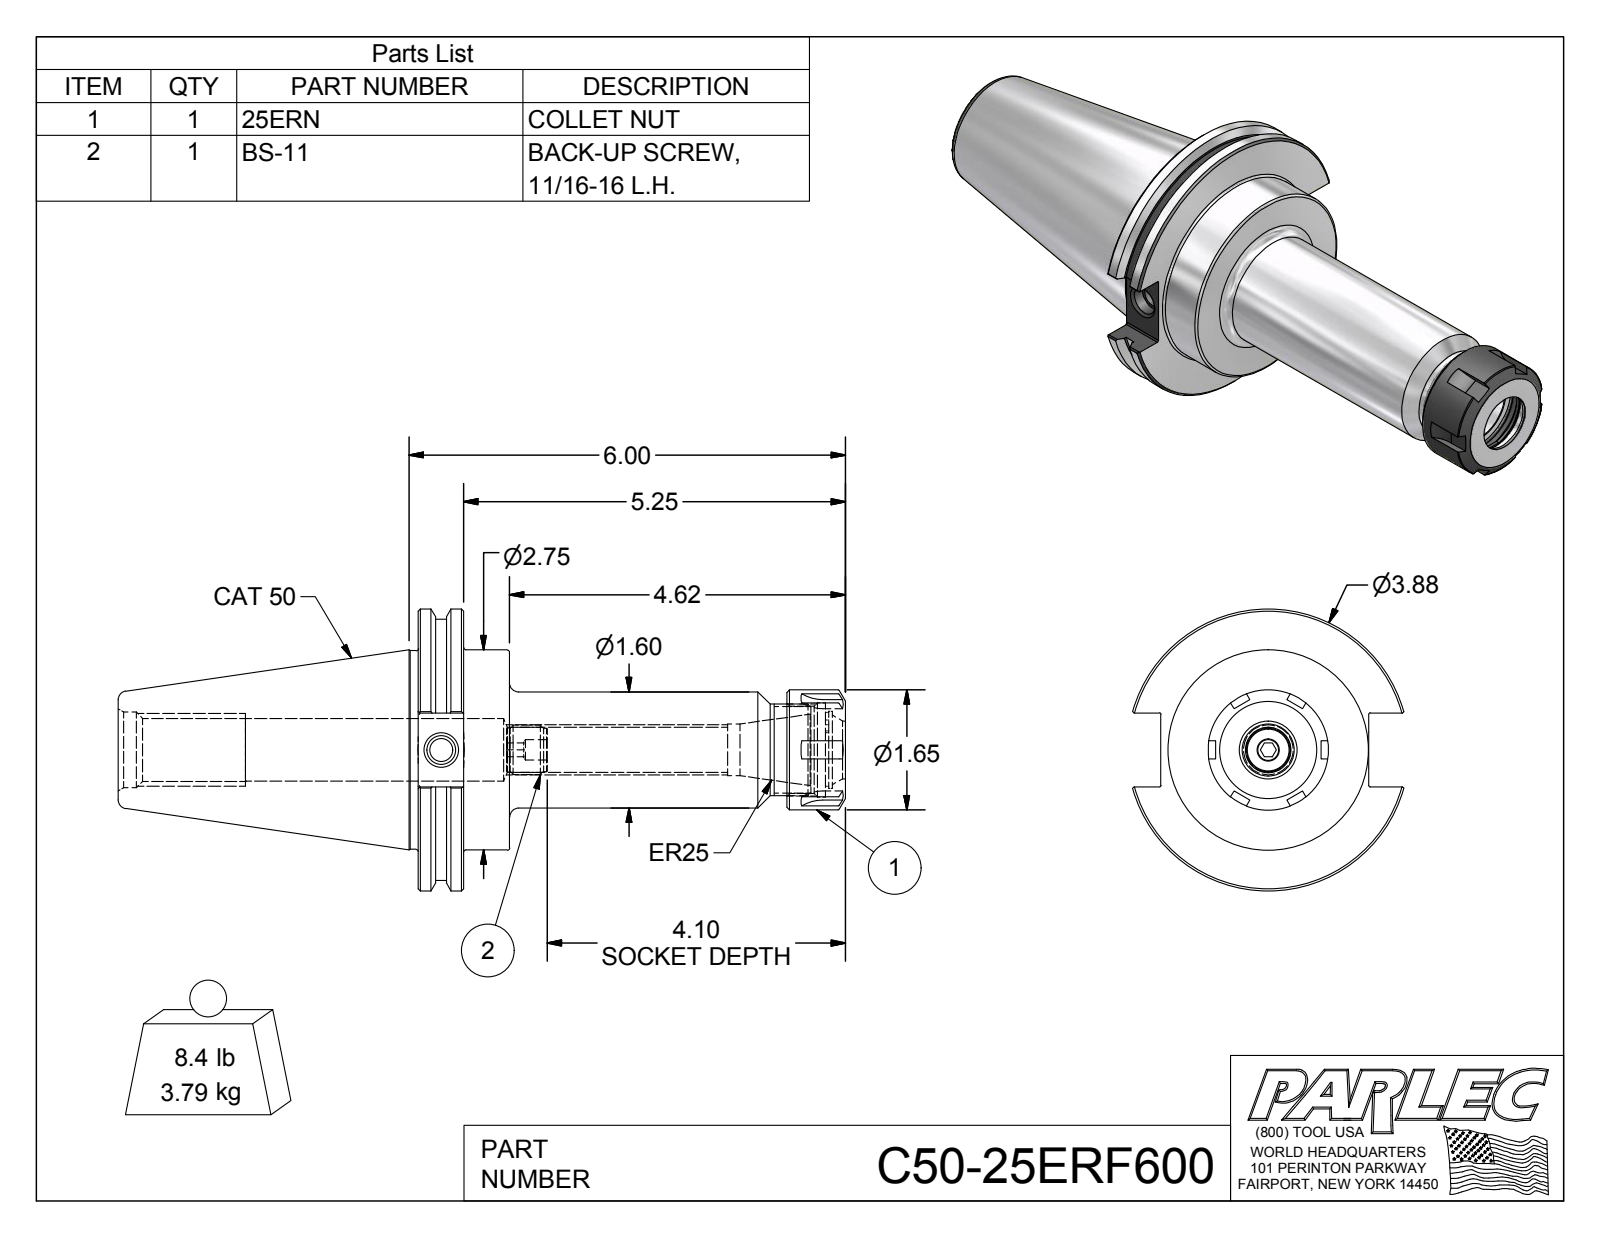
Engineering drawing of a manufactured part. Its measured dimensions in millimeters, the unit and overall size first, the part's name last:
Units: millimetres
Overall size (bounding box): 254 × 98.42 × 94.71
Round holes (diameter × count): ⌀7.11 ×1, ⌀8 ×1, ⌀10.13 ×1, ⌀15.75 ×1, ⌀18.03 ×1, ⌀20.32 ×1, ⌀21.95 ×1, ⌀21.97 ×1, ⌀26.37 ×1, ⌀30.5 ×1, ⌀32.88 ×1
Round bosses / shafts (diameter × count): ⌀98.42 ×1, ⌀91.29 ×1, ⌀69.85 ×1, ⌀69.34 ×1, ⌀42 ×1, ⌀40.51 ×1, ⌀32 ×1, ⌀17.3 ×1
Partial cylindrical surfaces — rounded edges, fillets, slot ends (radius × count): R0.51 ×20, R12 ×1, R13.06 ×1, R13.43 ×1
Main face-to-face distances: 15.88, 31.88, 16, 149.23, 133.35, 117.35, 128.66, 112.78, 96.78, 20.57
Volume: 492 035 mm³ · Surface area: 74 631 mm²
Bodies: 3 solids, 181 faces (72 planar, 48 cylindrical, 61 other)
Part name (STEP PRODUCT): C50-25ER6-1; 25ERN; BS-11; C50-25ERF600
STEP written by: Autodesk Inventor 2016 (AUTOMOTIVE_DESIGN)
